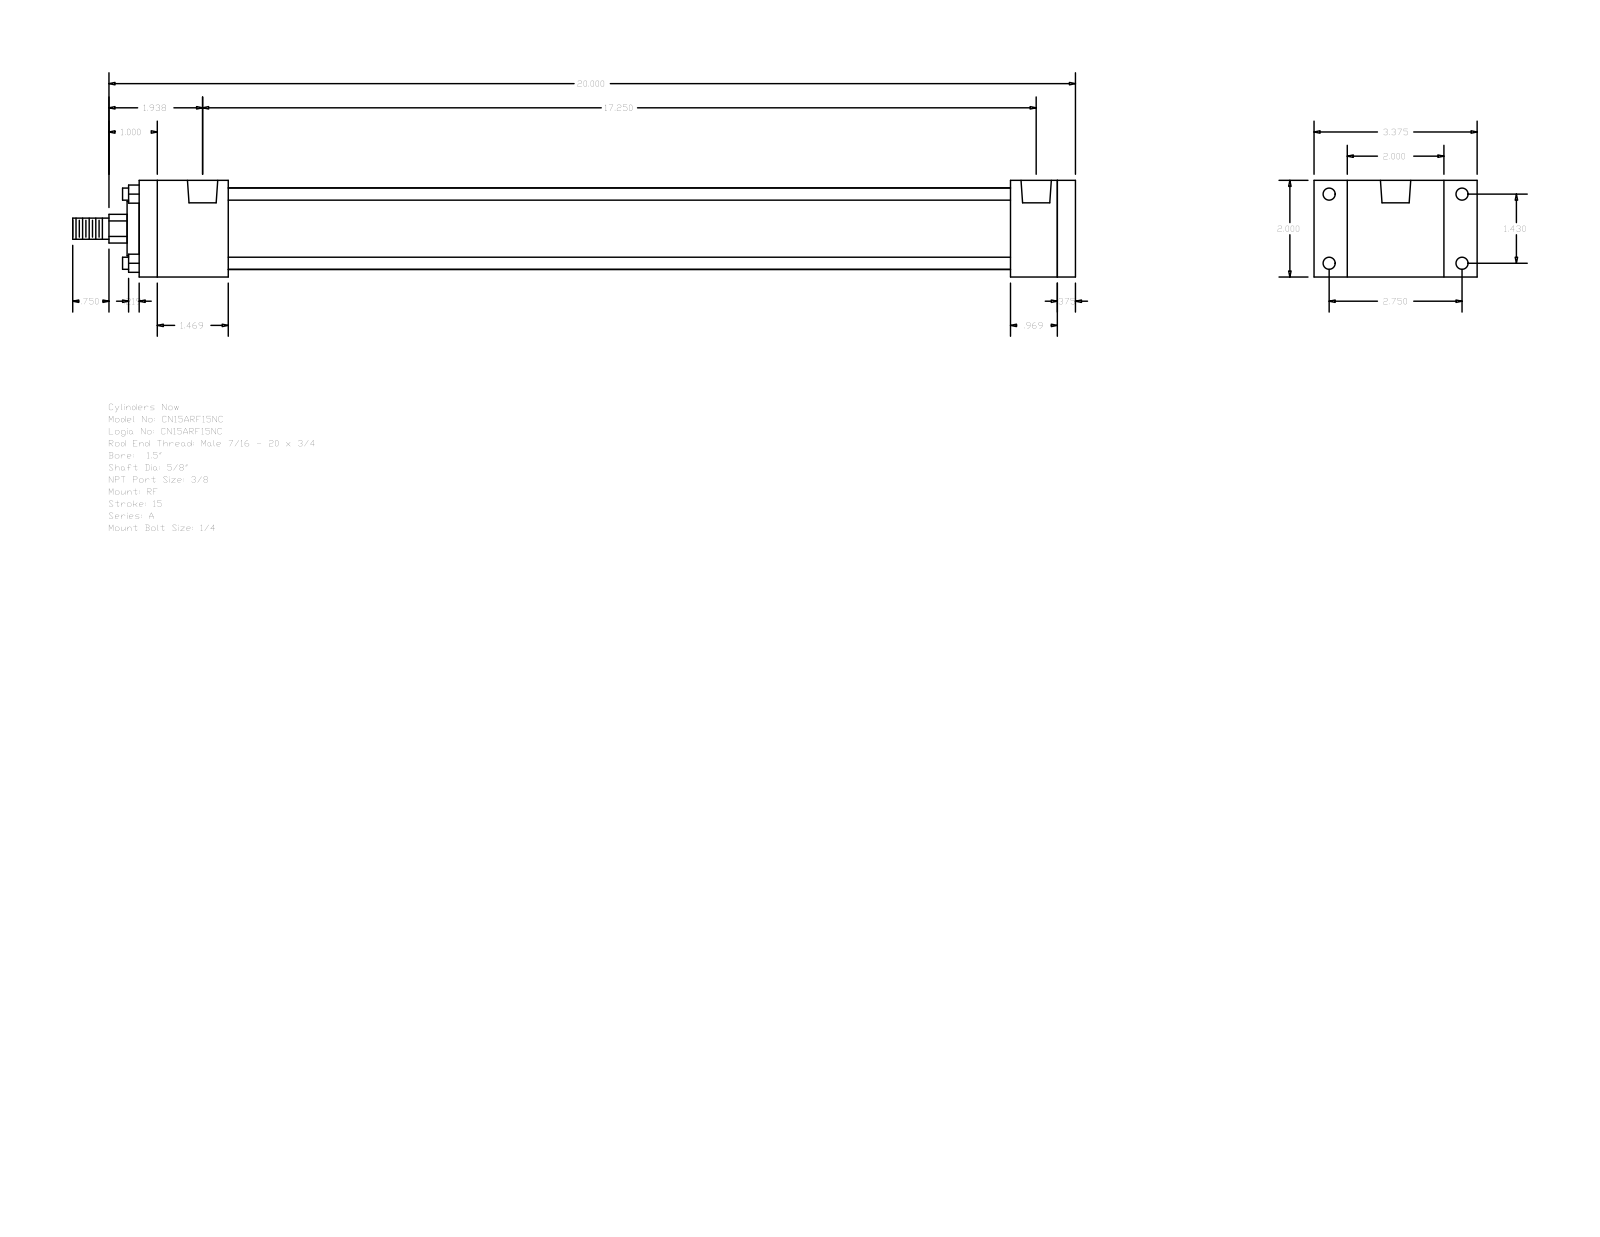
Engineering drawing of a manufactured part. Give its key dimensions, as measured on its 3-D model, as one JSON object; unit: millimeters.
{"part_name": "A_RF__0150_0.625", "step_written_by": "GSSL Pune (CONFIG_CONTROL_DESIGN)", "units": "millimeters", "bodies": {"solids": 0, "faces": 92, "planar": 64, "cylindrical": 28, "other": 0}, "overall_size": [527.05, 85.72, 50.8], "round_holes": [[5.56, 4], [6.35, 4], [15.93, 2]], "round_bosses_or_shafts": [[6.35, 4], [42.93, 1], [28.57, 1], [15.88, 1], [11.11, 1]], "partial_cylinders_radius": [[7.54, 1]], "face_to_face_distances": [50.8, 9.52, 482.6, 492.12, 457.99, 24.61, 34.13, 46.83, 411.16, 435.77], "hole_center_spacings": [3.97, 36.32, 69.84, 78.72, 430.21, 434.18, 438.15]}
